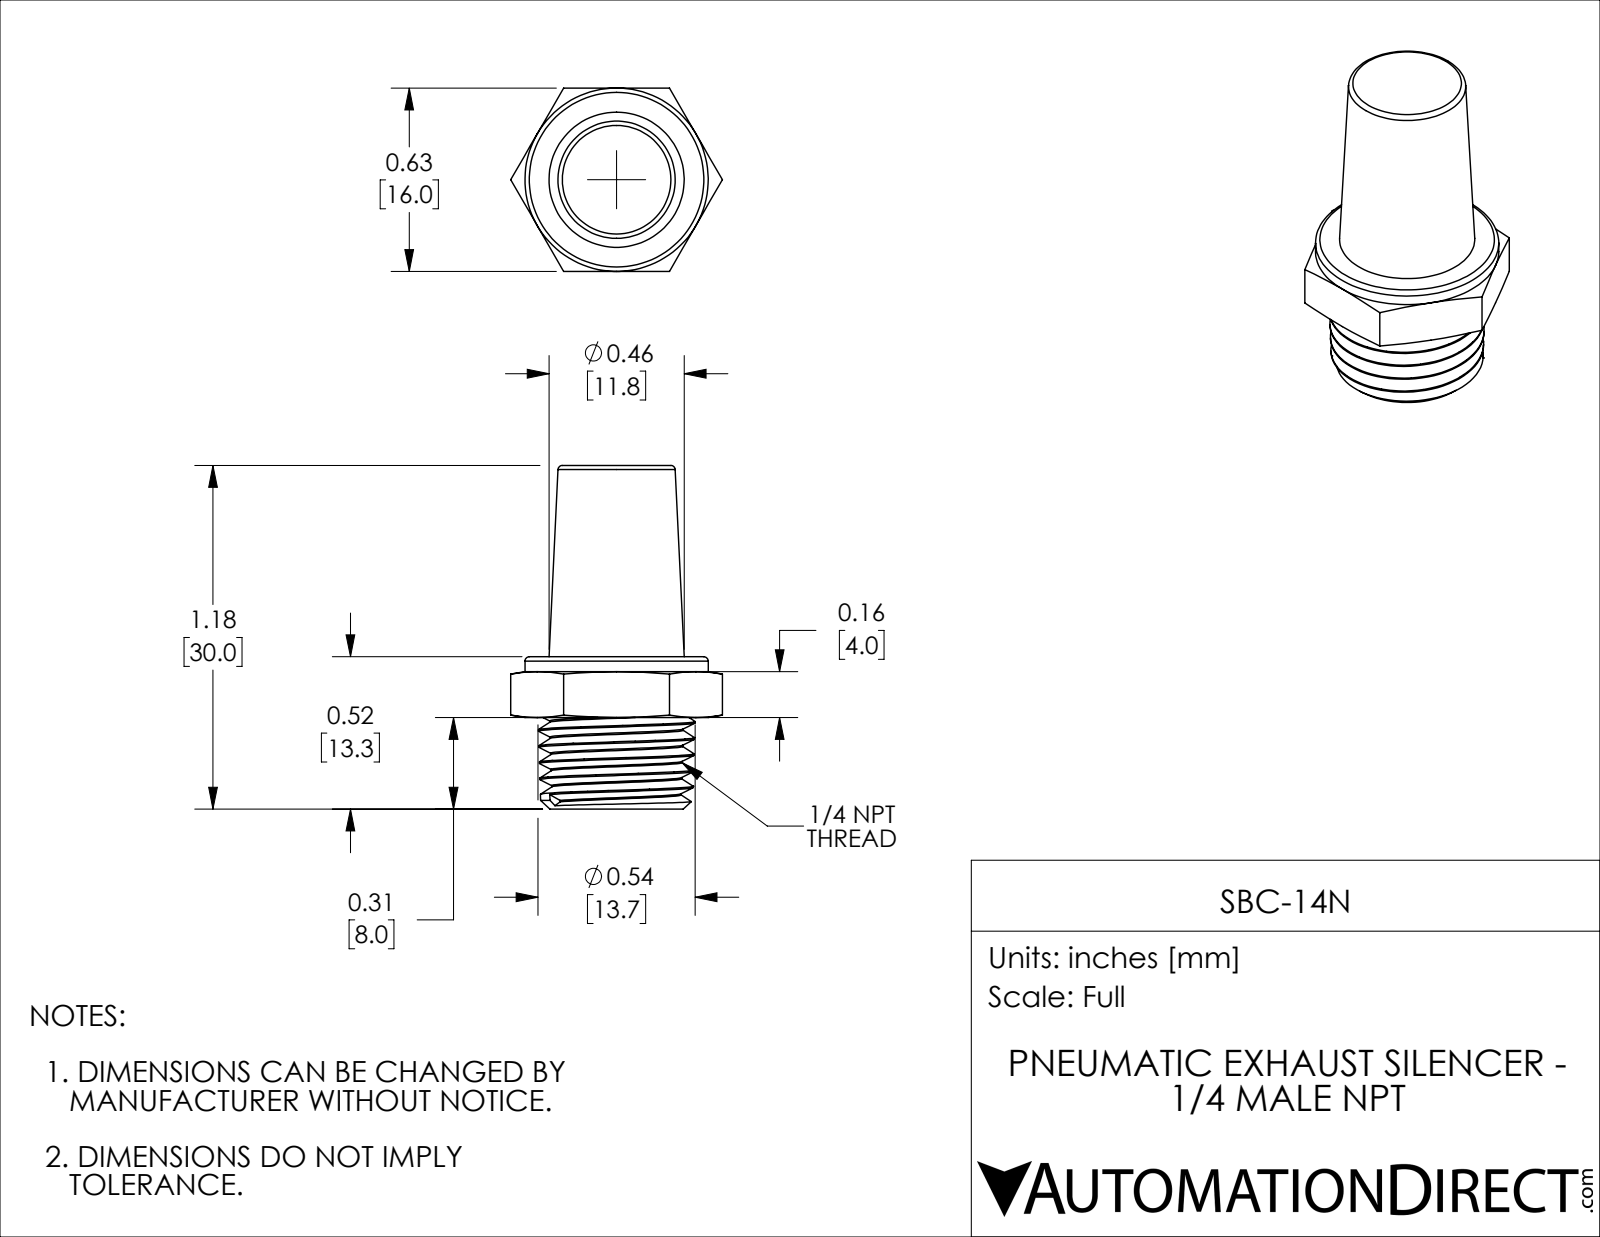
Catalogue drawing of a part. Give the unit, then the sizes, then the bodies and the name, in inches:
Units: inches
Overall size (bounding box): 1.181 × 0.727 × 0.63
Round holes (diameter × count): ⌀0.314 ×1
Round bosses / shafts (diameter × count): ⌀0.63 ×1
Main face-to-face distances: 0.63, 0.209, 0.866, 0.657, 0.315, 0.524, 1.181, 0.5, 0.185, 0.024
Volume: 0.188 in³ · Surface area: 3.278 in²
Bodies: 1 solid, 52 faces (12 planar, 4 cylindrical, 36 other)
Part name (STEP PRODUCT): SBC-14N
STEP written by: SolidWorks 2021 (CONFIG_CONTROL_DESIGN)
